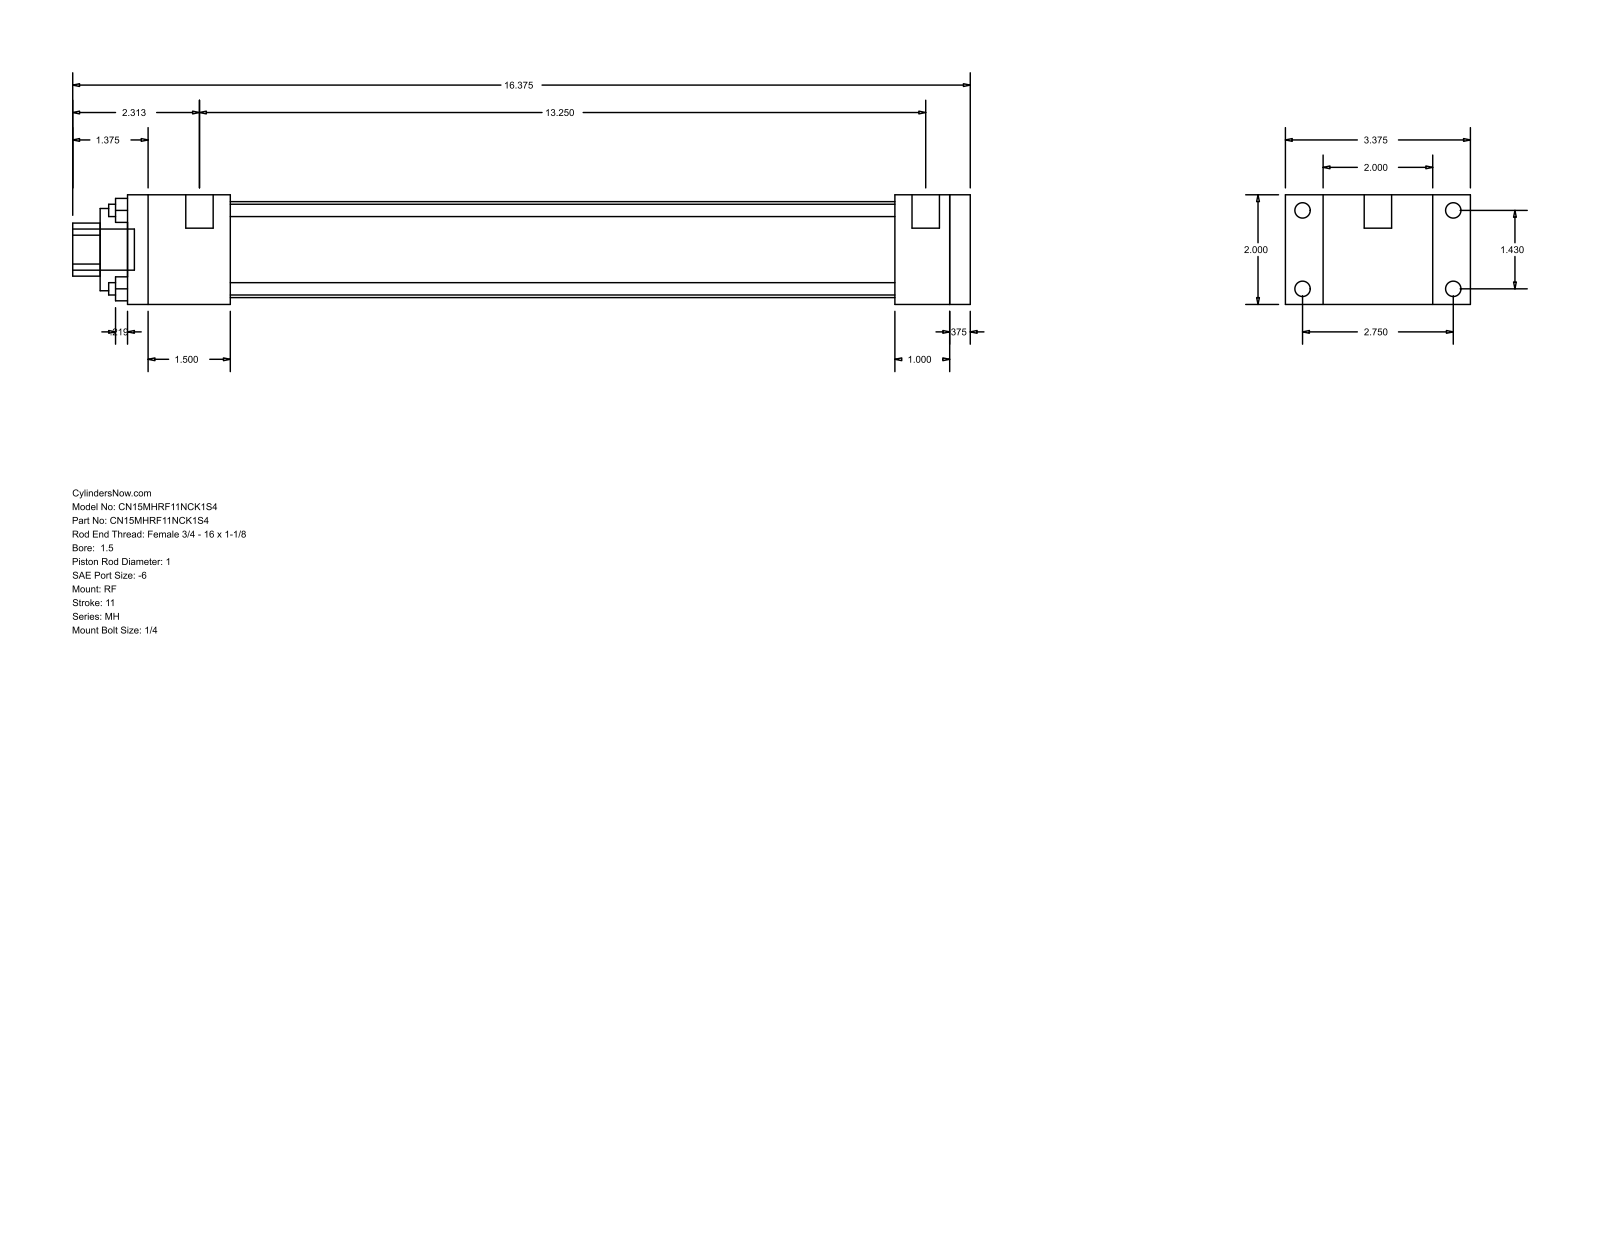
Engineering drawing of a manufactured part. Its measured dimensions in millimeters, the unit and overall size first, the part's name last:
Units: millimetres
Overall size (bounding box): 415.93 × 85.72 × 50.8
Round holes (diameter × count): ⌀5.71 ×4, ⌀25.4 ×1, ⌀38.1 ×1, ⌀44.45 ×1
Round bosses / shafts (diameter × count): ⌀7.14 ×4, ⌀5.56 ×4, ⌀12.7 ×2, ⌀19.05 ×1
Partial cylindrical surfaces — rounded edges, fillets, slot ends (radius × count): R12.29 ×1
Main face-to-face distances: 50.8, 9.53, 381, 25.4, 390.53, 17.46, 68.26, 355.6, 34.93, 47.63
Hole centre spacings: 25.68, 36.32, 51.36
Bodies: 0 solids, 92 faces (64 planar, 28 cylindrical, 0 other)
Part name (STEP PRODUCT): MH_RF__0150_1
STEP written by: GSSL Pune (CONFIG_CONTROL_DESIGN)
